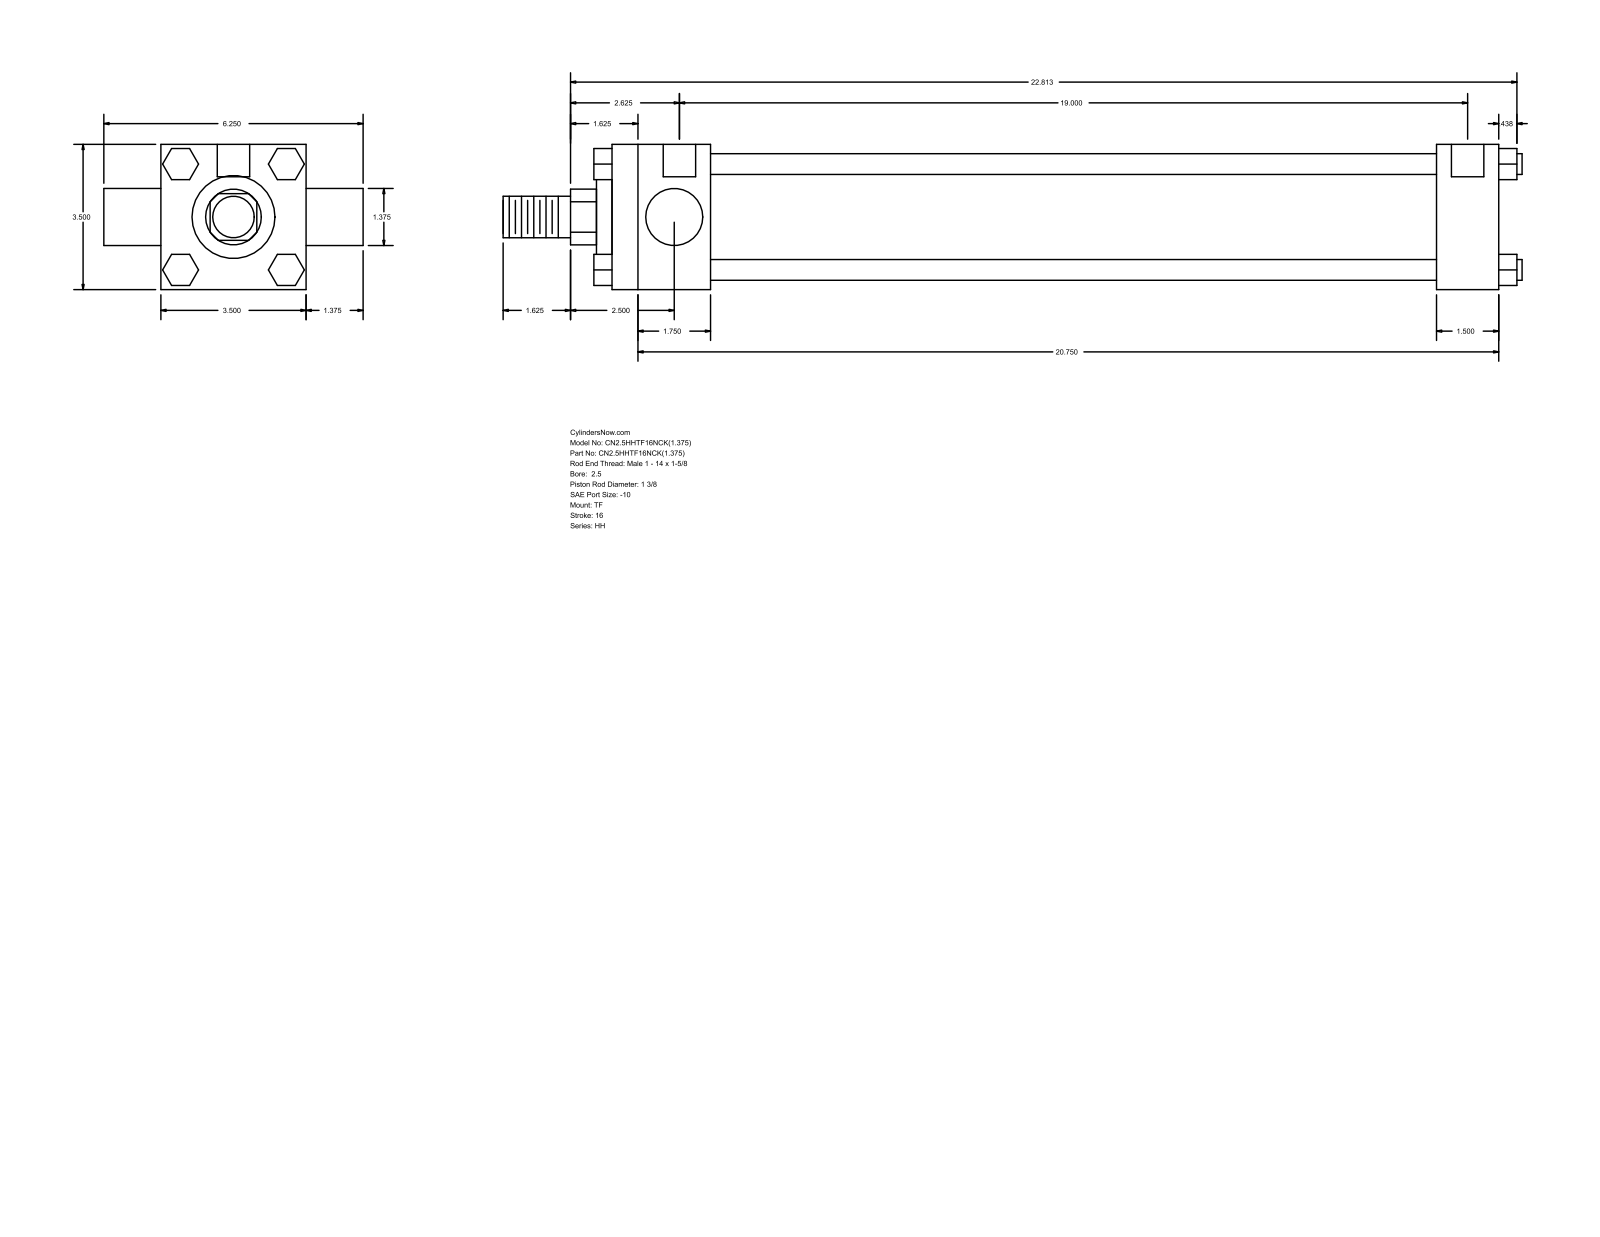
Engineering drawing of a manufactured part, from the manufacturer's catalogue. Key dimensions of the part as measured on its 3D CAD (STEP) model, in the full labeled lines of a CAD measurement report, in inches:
Part name (STEP PRODUCT): HH_TF__0250_1.375
STEP written by: GSSL Pune (CONFIG_CONTROL_DESIGN)
Units: inches
Bodies: 0 solids, 120 faces (92 planar, 28 cylindrical, 0 other)
Overall size (bounding box): 24.563 × 6.25 × 3.5
Round holes (diameter × count): ⌀0.219 ×3, ⌀0.781 ×2
Round bosses / shafts (diameter × count): ⌀0.5 ×4, ⌀1.375 ×2, ⌀2.875 ×1, ⌀2 ×1, ⌀1 ×1
Partial cylindrical surfaces — rounded edges, fillets, slot ends (radius × count): R0.672 ×1
Main face-to-face distances: 3.5, 21.375, 2.375, 19, 19.875, 17.5, 1.5, 0.75, 1.275, 2.208
Hole centre spacings: 0.062, 0.063, 19, 19.062, 19.063, 19.125
